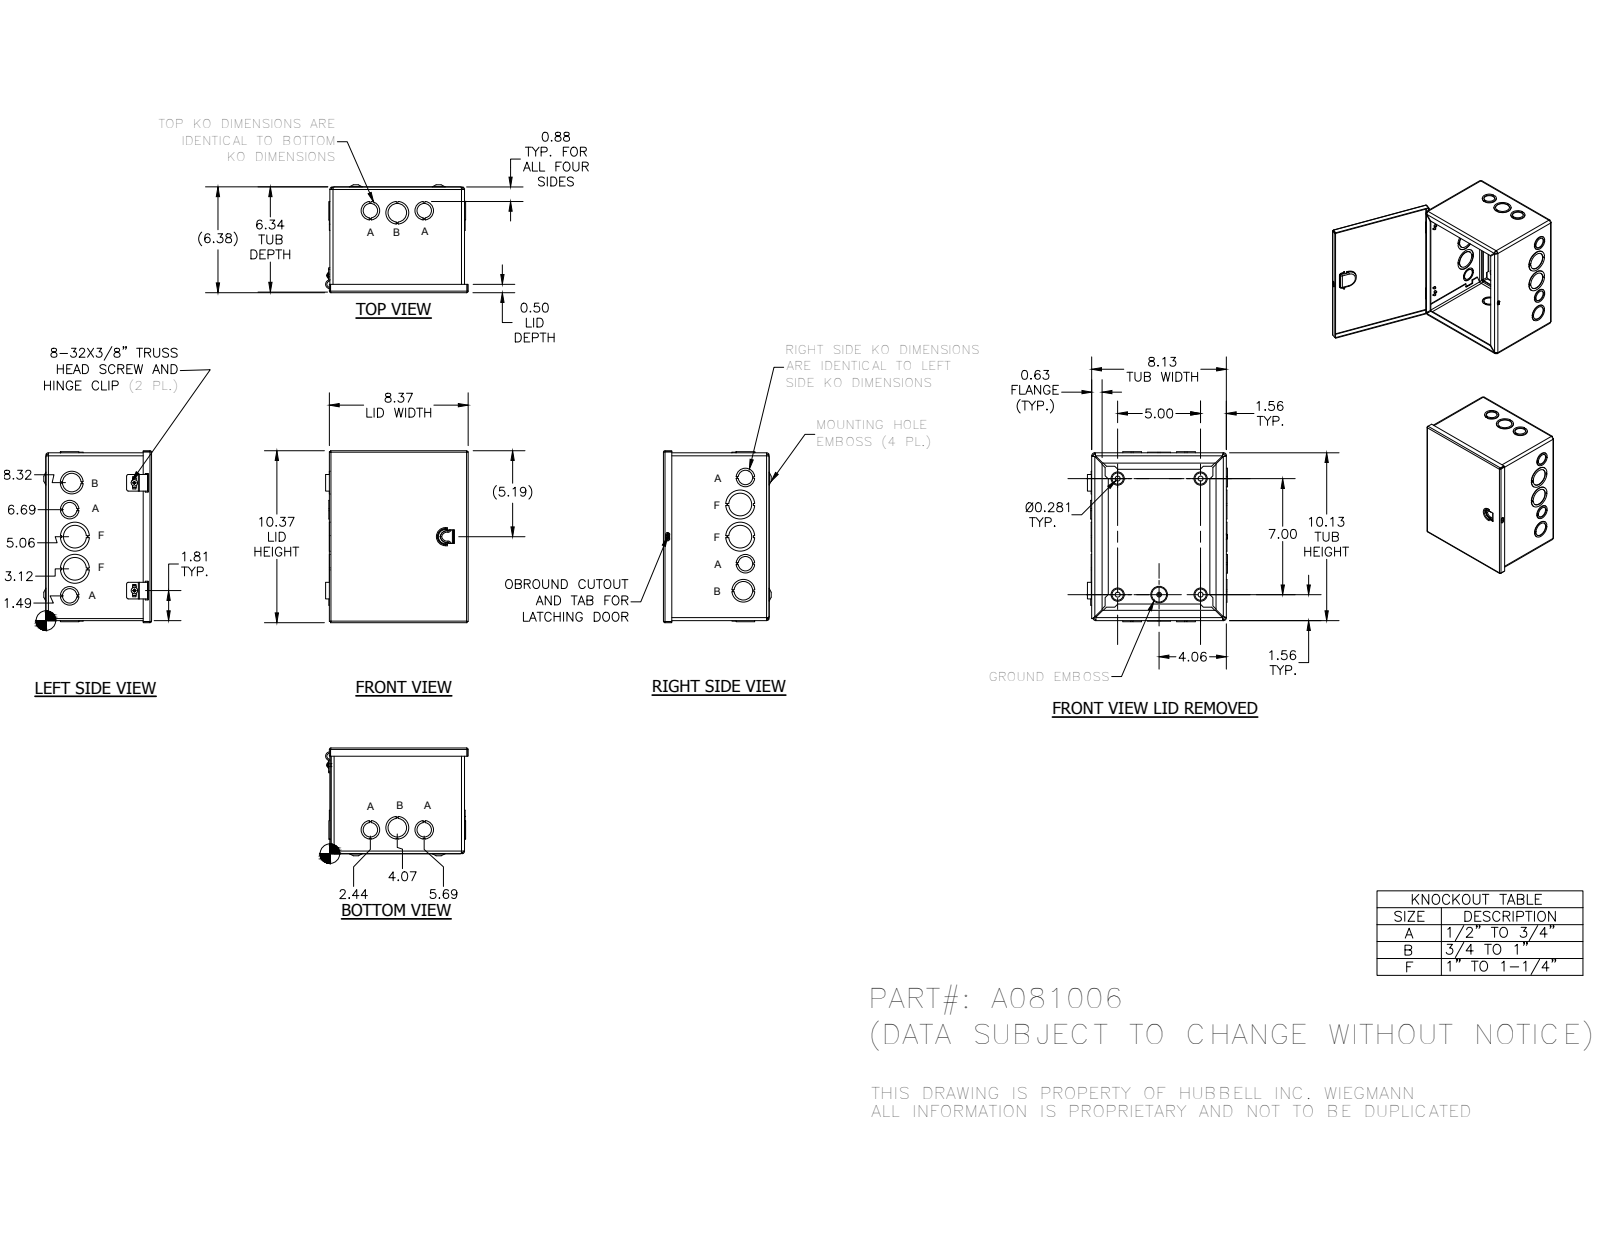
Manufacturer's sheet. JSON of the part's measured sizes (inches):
{"part_name": "A0810BA; A081006WRA; 31816; 372177 (+3 more)", "step_written_by": "Autodesk Inventor 2014 (AUTOMOTIVE_DESIGN)", "units": "inches", "bodies": {"solids": 23, "faces": 943, "planar": 582, "cylindrical": 203, "other": 158}, "overall_size": [10.437, 8.637, 6.504], "round_holes": [[1.125, 9], [0.875, 6], [1.375, 6], [0.3, 4], [1.75, 3], [0.14, 2], [0.165, 1]], "round_bosses_or_shafts": [[0.384, 2], [0.164, 2], [0.228, 1]], "partial_cylinders_radius": [[0.125, 15], [0.031, 10], [0.063, 9], [0.094, 8], [0.187, 8], [0.055, 4], [0.062, 4], [0.07, 4]], "face_to_face_distances": [0.062, 0.062, 8.063, 6.316, 6.254, 0.063, 6.317, 6.379, 8.125, 8.001], "hole_center_spacings": [1.659, 1.94, 3.584, 1.333, 2.5, 3.781, 3.824, 3.919]}
